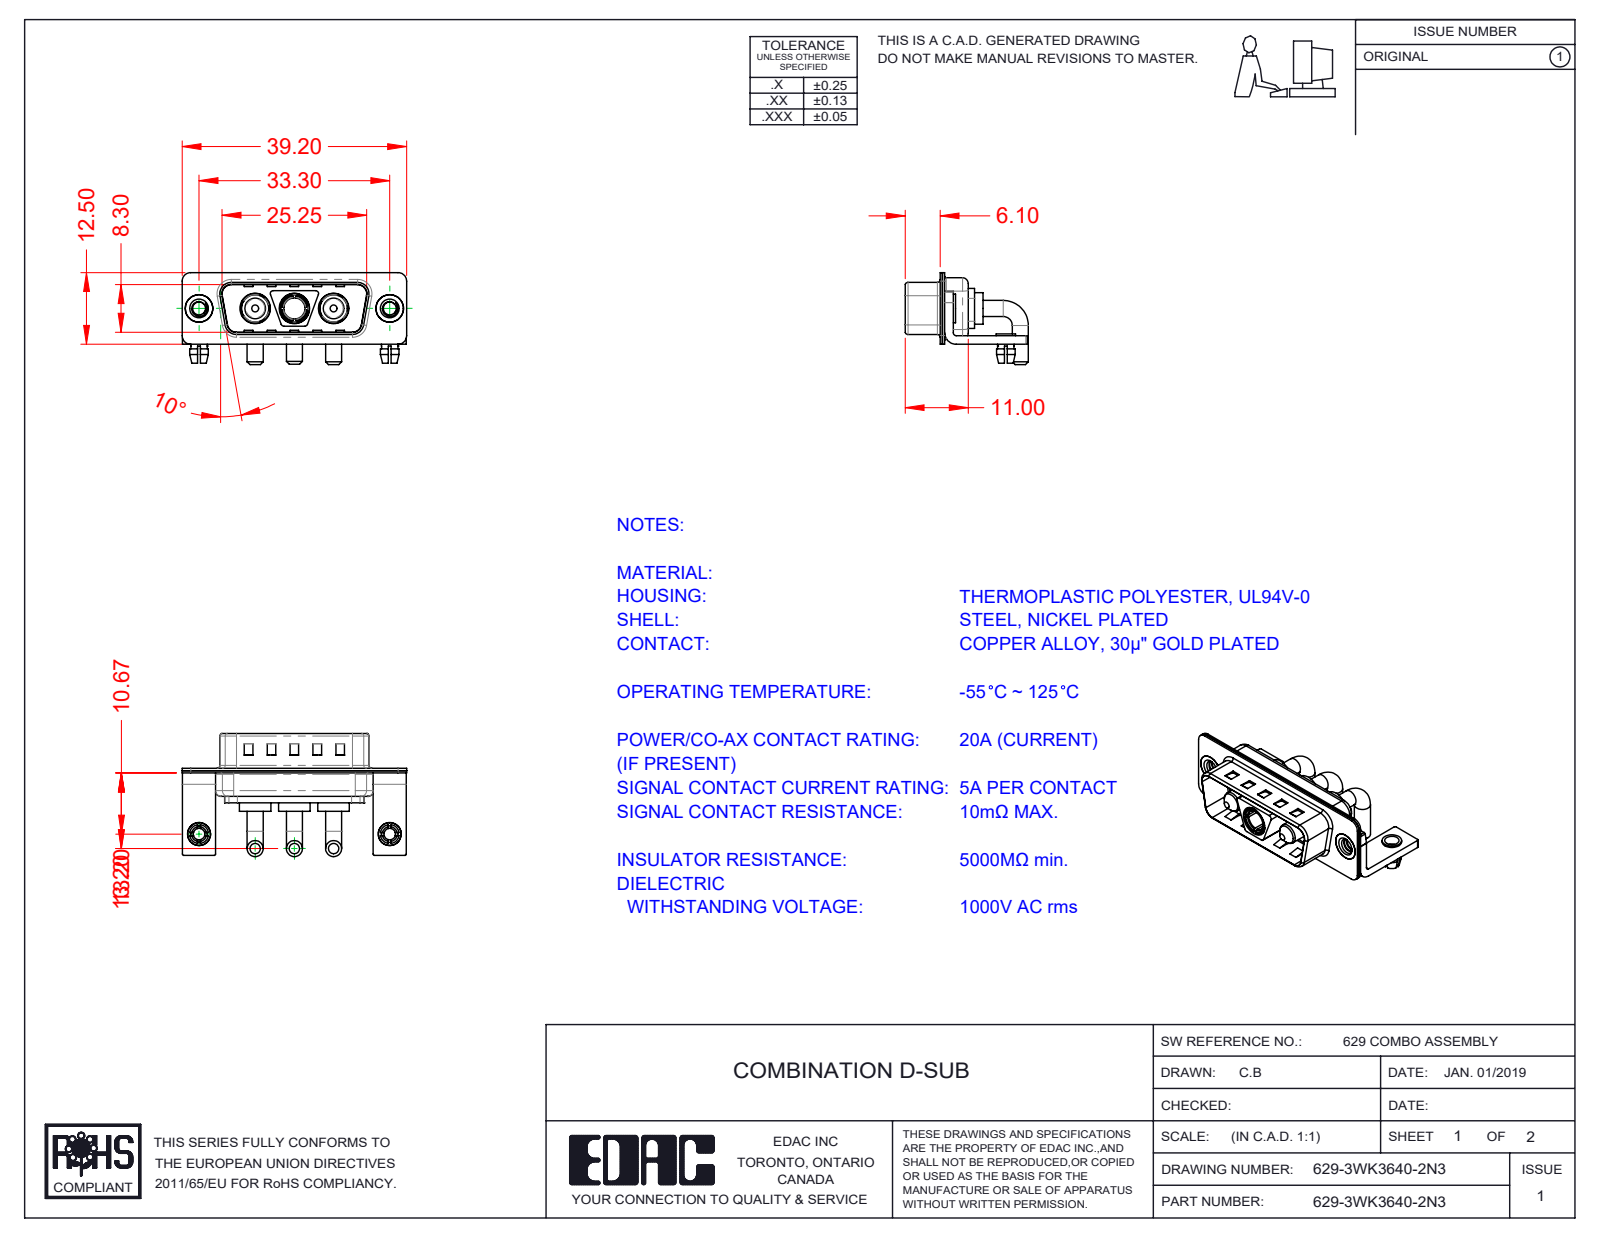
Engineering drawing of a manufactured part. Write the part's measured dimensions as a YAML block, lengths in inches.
part_name: "629Combo Board Lock; 629Combo Housing_3WK3; 629Combo Threaded Rivet_3; 629Combo Shell Rear_15 Contacts (+5 more)"
step_written_by: "SolidWorks 2020 (CONFIG_CONTROL_DESIGN)"
units: inches
bodies: {solids: 15, faces: 646, planar: 261, cylindrical: 255, other: 130}
overall_size: [1.543, 0.846, 0.632]
volume: 0.162
surface_area: 9.548
round_holes:
  - {diameter: 0.191, count: 3}
  - {diameter: 0.209, count: 3}
  - {diameter: 0.079, count: 2}
  - {diameter: 0.089, count: 2}
  - {diameter: 0.098, count: 2}
  - {diameter: 0.126, count: 2}
  - {diameter: 0.157, count: 2}
  - {diameter: 0.189, count: 2}
  - {diameter: 0.146, count: 1}
round_bosses_or_shafts:
  - {diameter: 0.11, count: 6}
  - {diameter: 0.217, count: 3}
  - {diameter: 0.205, count: 3}
  - {diameter: 0.187, count: 3}
  - {diameter: 0.148, count: 3}
  - {diameter: 0.197, count: 2}
  - {diameter: 0.193, count: 2}
  - {diameter: 0.157, count: 2}
partial_cylinders:
  - {radius: 0.01, count: 16}
  - {radius: 0.059, count: 16}
  - {radius: 0.02, count: 13}
  - {radius: 0.079, count: 13}
  - {radius: 0.063, count: 8}
  - {radius: 0.024, count: 4}
  - {radius: 0.026, count: 4}
  - {radius: 0.035, count: 4}
face_to_face_distances: [0.016, 0.031, 0.059, 0.374, 0.358, 0.343, 0.39, 0.205, 0.024, 0.409]
hole_center_spacings: [0.27, 0.386, 0.656, 0.925, 1.311, 0.539]
